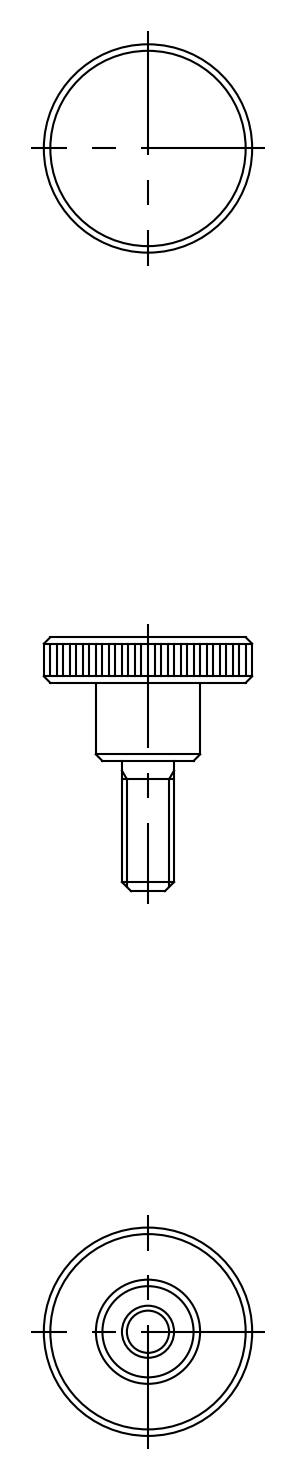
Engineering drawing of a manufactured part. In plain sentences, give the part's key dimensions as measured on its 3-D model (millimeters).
The part is named "knob". Its 3-D file was written by "CADfix (AUTOMOTIVE_DESIGN)". It is 1 solid with 18 faces: 0 planar, 0 cylindrical and 18 other. Overall it measures 19.5 by 16 by 16 millimeters. Its volume is 1 115 cubic millimeters and its surface area 811 square millimeters.
